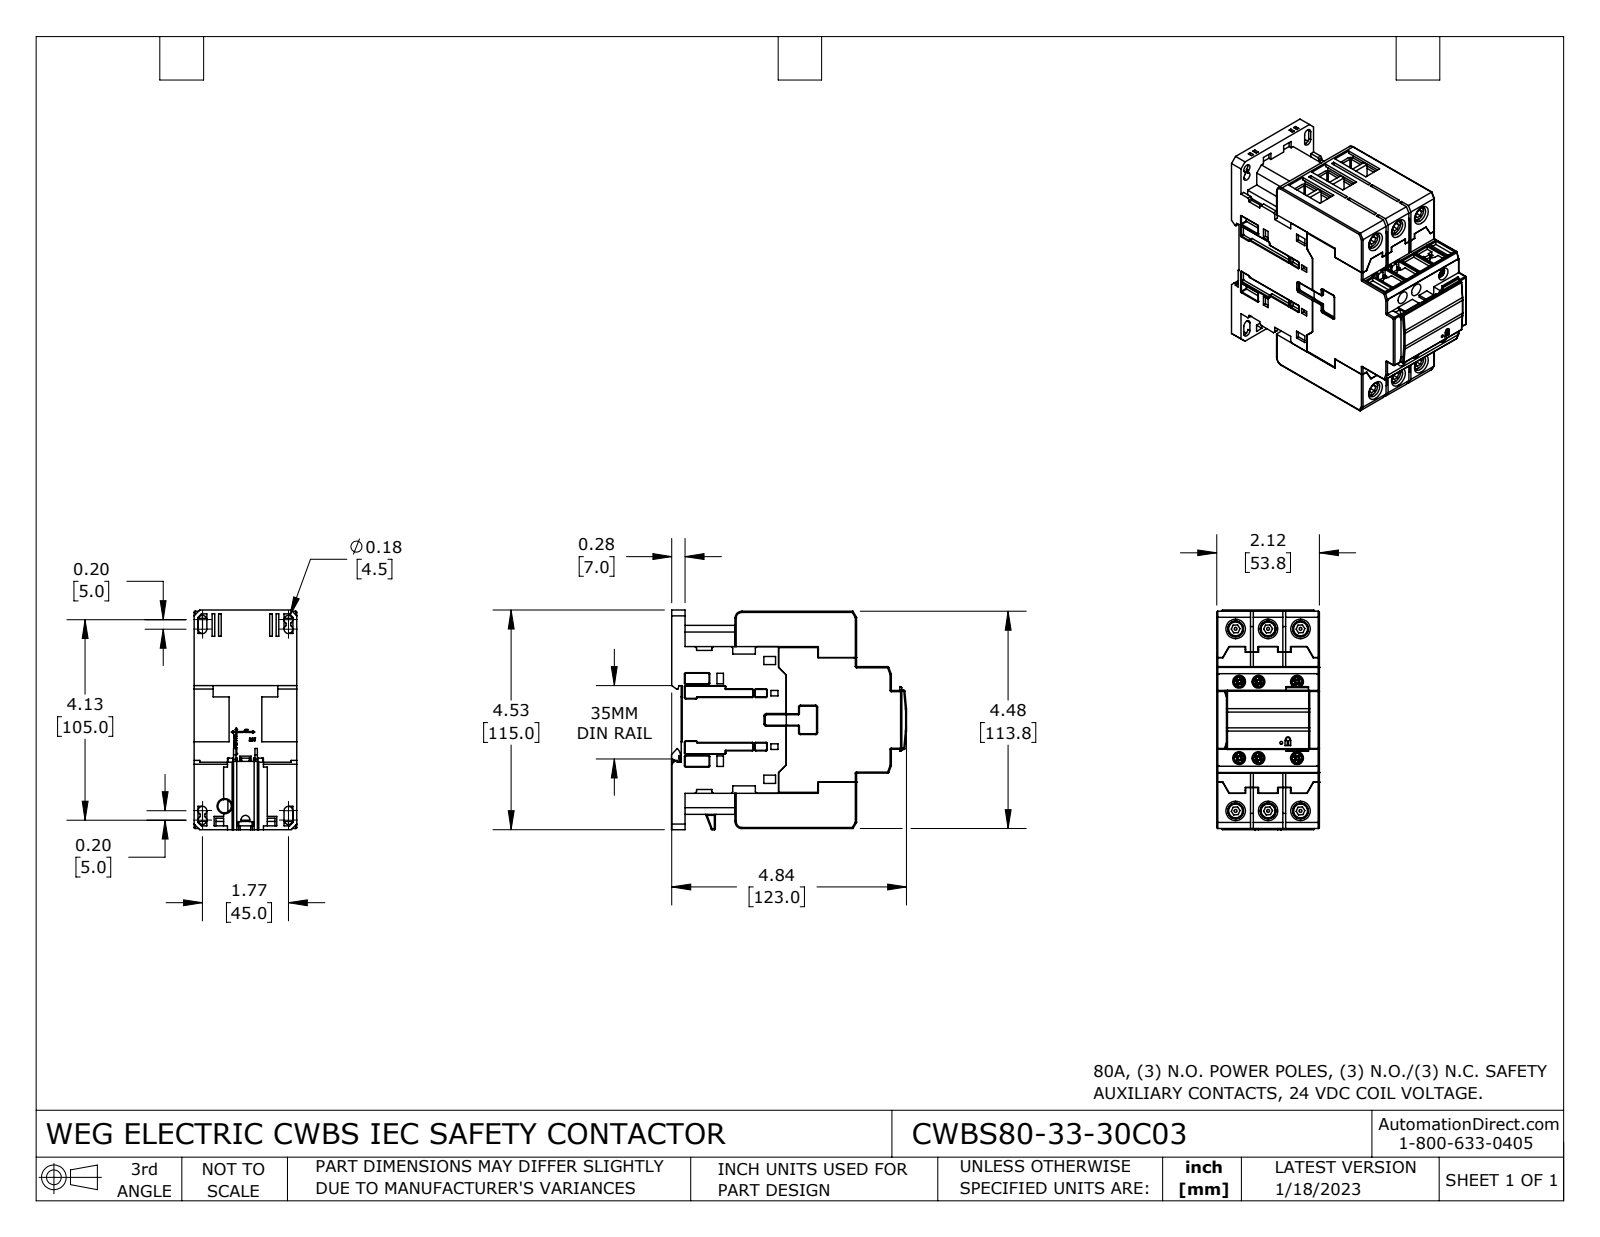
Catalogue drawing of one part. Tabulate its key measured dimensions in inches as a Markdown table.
| quantity | value |
| --- | --- |
| part name | CWBS80-33-30C03 |
| STEP written by | SolidWorks 2021 (CONFIG_CONTROL_DESIGN) |
| units | inches |
| bodies | 37 solids, 2637 faces (1669 planar, 550 cylindrical, 418 other) |
| overall size | 4.846 × 4.528 × 2.118 |
| volume | 33.67 in³ |
| surface area | 209.3 in² |
| round holes (diameter × count) | 0.124 × 6, 0.197 × 6, 0.264 × 6, 0.323 × 6, 0.177 × 4, 0.125 × 2, 0.276 × 2, 0.059 × 1 |
| round bosses / shafts (diameter × count) | 0.343 × 6, 0.236 × 6, 0.135 × 6 |
| partial cylindrical surfaces (radius × count) | 0.02 × 89, 0.012 × 69, 0.004 × 48, 0.024 × 42, 0.079 × 18, 0.089 × 5, 0.039 × 3, 0.059 × 3 |
| main face-to-face distances | 0.059, 2.118, 0.669, 0.728, 3.024, 3.752, 0.108, 0.217, 3.811, 0.098 |
| hole center spacings | 0.669, 1.091, 1.241, 1.669, 2.665, 2.73, 2.949, 3.811 |
